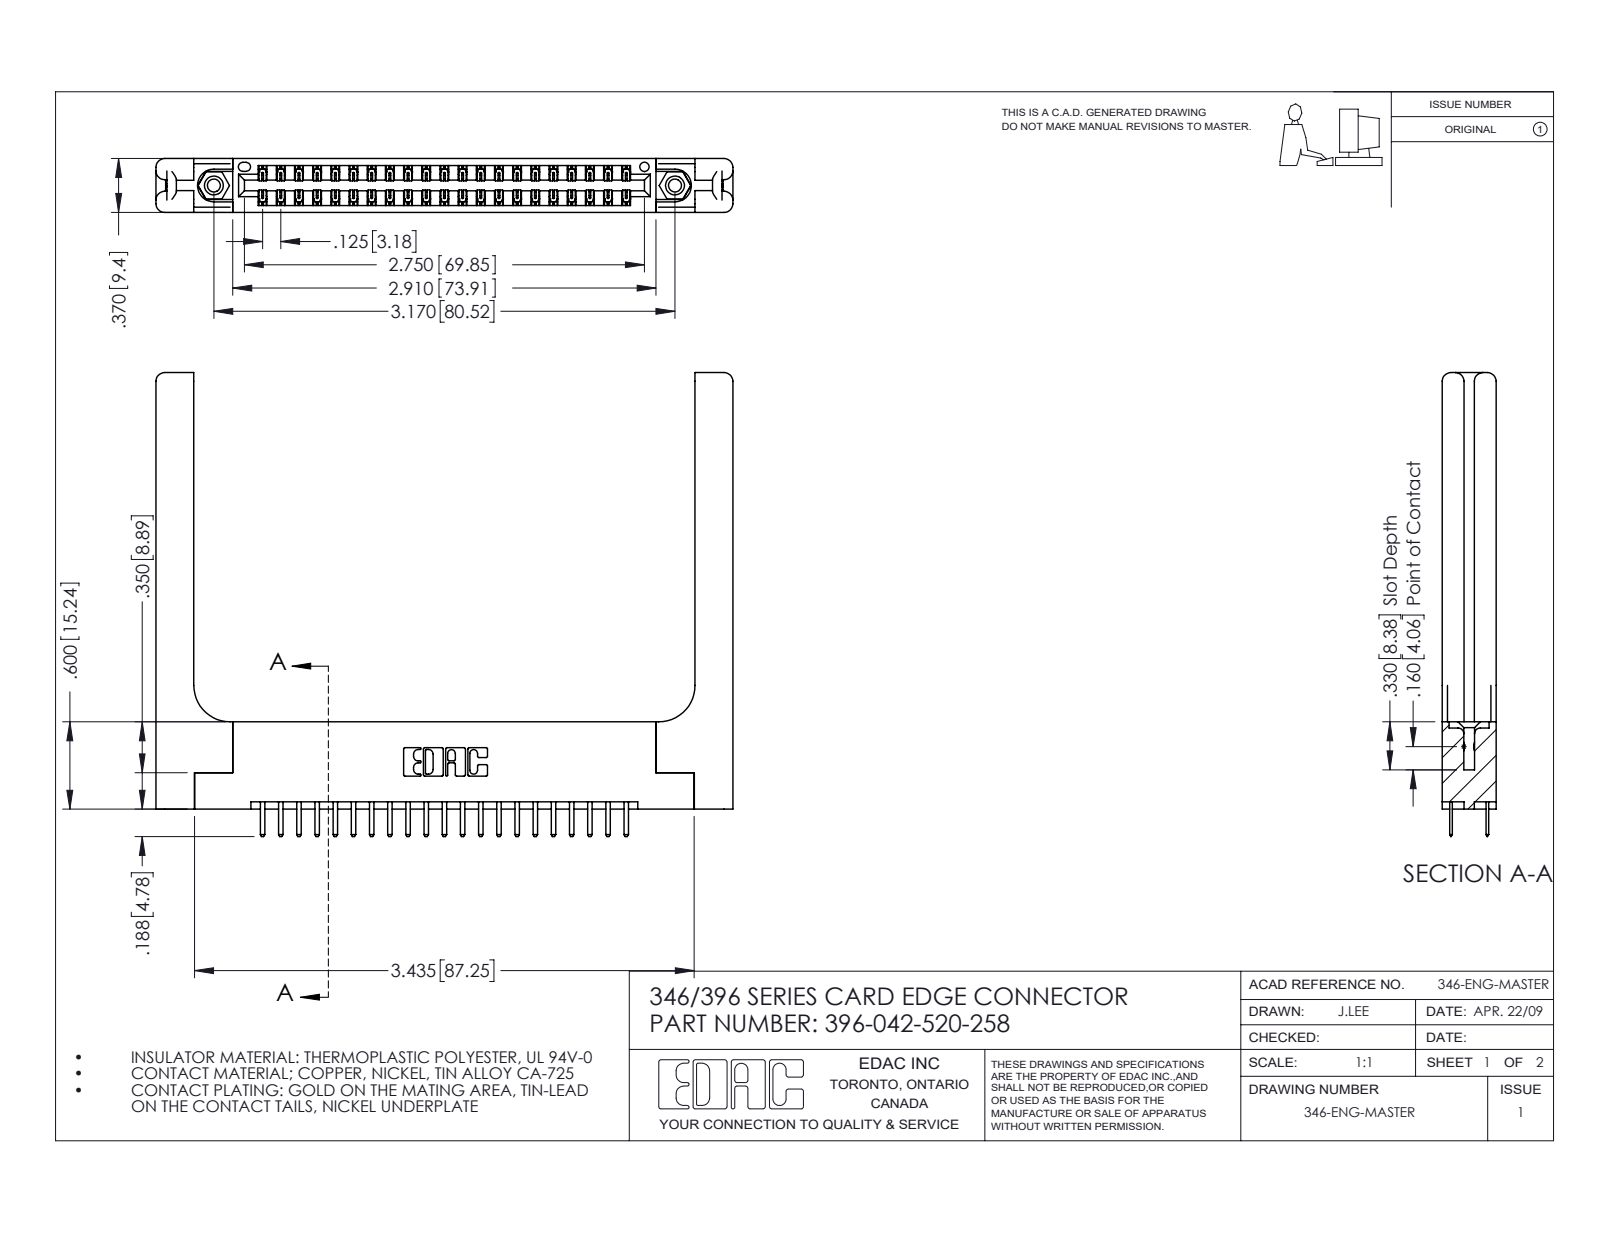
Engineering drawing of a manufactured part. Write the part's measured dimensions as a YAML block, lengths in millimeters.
part_name: "345-250-001_345-250-001-102; 396-042-520-258; 346-220-058_345-220-058; 345-292-001_345-293-120 (+1 more)"
step_written_by: "SolidWorks 2016 (CONFIG_CONTROL_DESIGN)"
units: millimeters
bodies: {solids: 47, faces: 2730, planar: 1778, cylindrical: 892, other: 60}
overall_size: [100.7, 81, 9.4]
volume: 17140
surface_area: 17850
round_holes:
  - {diameter: 2.3, count: 2}
  - {diameter: 3.2, count: 2}
  - {diameter: 4, count: 2}
  - {diameter: 1.6, count: 1}
round_bosses_or_shafts:
  - {diameter: 3.9, count: 2}
partial_cylinders:
  - {radius: 0.2, count: 63}
  - {radius: 0.3, count: 46}
  - {radius: 0.3, count: 22}
  - {radius: 1.5, count: 16}
  - {radius: 0.2, count: 6}
  - {radius: 0.8, count: 6}
  - {radius: 0.7, count: 3}
  - {radius: 0.4, count: 2}
face_to_face_distances: [9.4, 1.8, 3.8, 3.8, 1.2, 8.2, 6.4, 2, 2.6, 5.6]
hole_center_spacings: [6.2, 75.3, 80.5]
